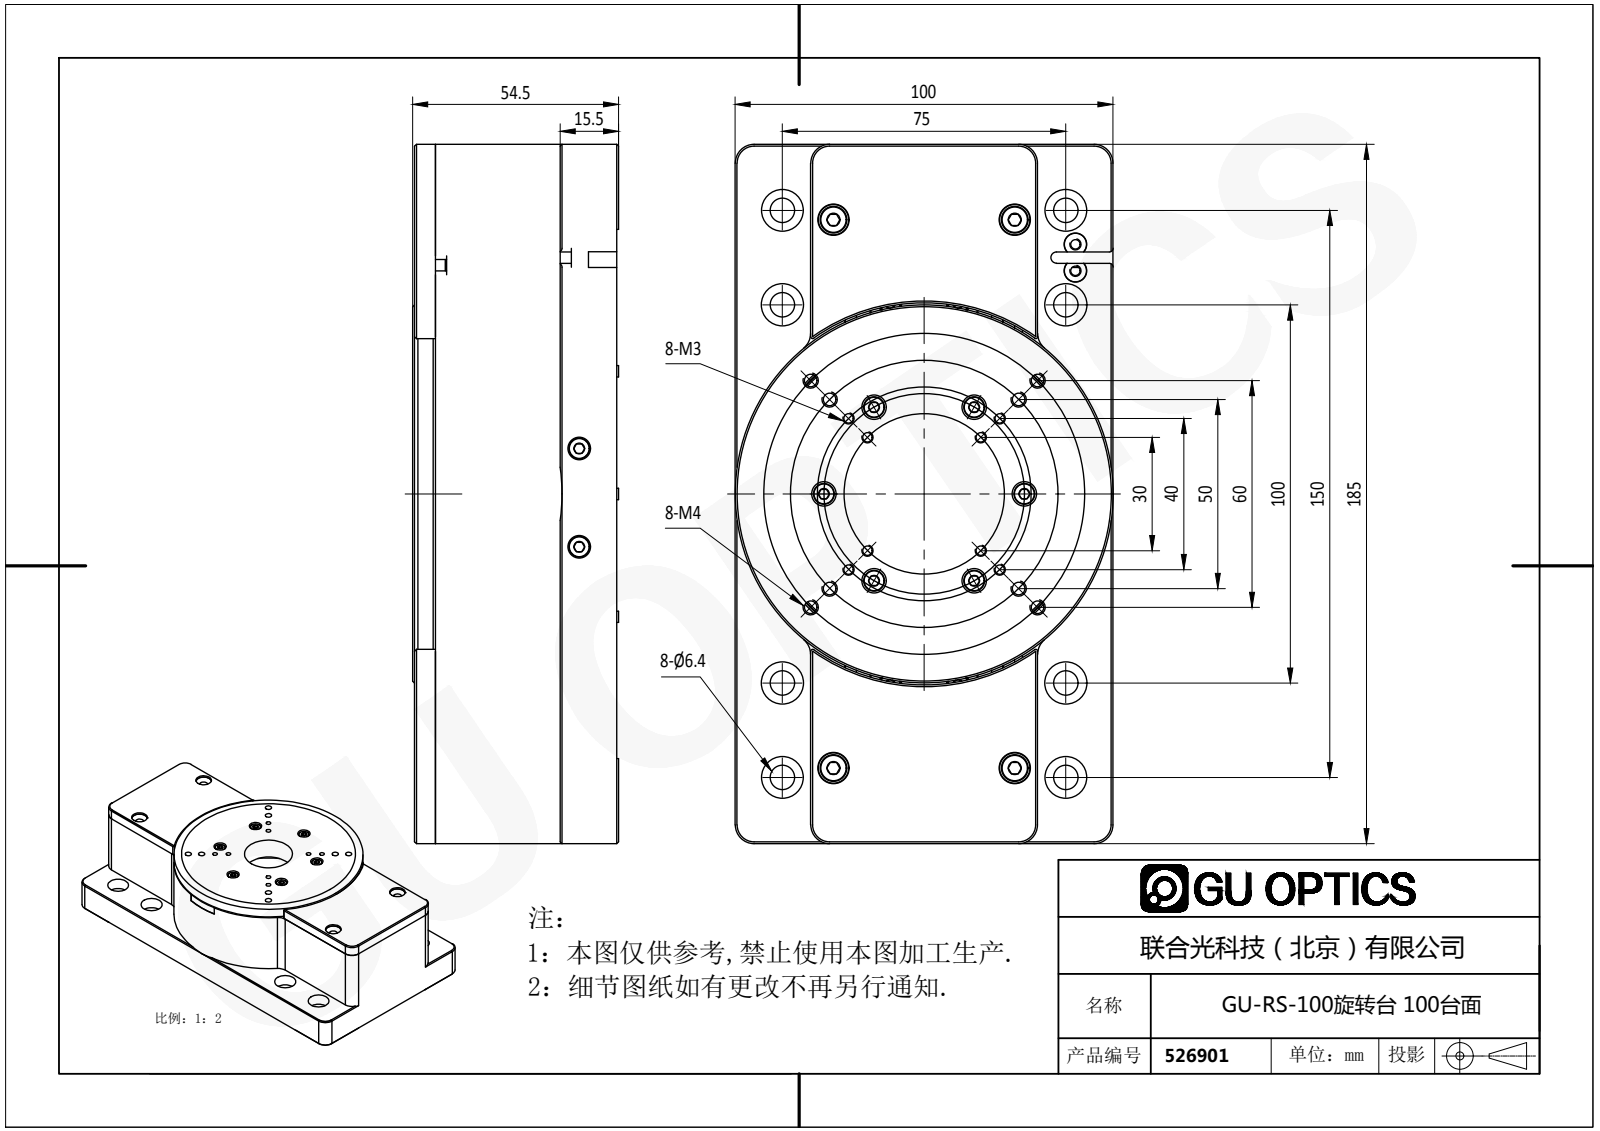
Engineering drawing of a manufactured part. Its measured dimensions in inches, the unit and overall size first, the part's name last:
Units: inches
Overall size (bounding box): 7.283 × 3.937 × 2.146
Round holes (diameter × count): ⌀0.098 ×40, ⌀0.13 ×12, ⌀0.252 ×8, ⌀0.126 ×6, ⌀0.256 ×6, ⌀0.081 ×4, ⌀0.106 ×4, ⌀0.118 ×4, ⌀0.157 ×4, ⌀0.169 ×4, ⌀0.197 ×4, ⌀0.325 ×4
Round bosses / shafts (diameter × count): ⌀0.118 ×48, ⌀0.217 ×8, ⌀0.157 ×8, ⌀0.128 ×4, ⌀0.098 ×4, ⌀0.097 ×4, ⌀0.097 ×4, ⌀3.937 ×1
Partial cylindrical surfaces — rounded edges, fillets, slot ends (radius × count): R0.118 ×30, R0.039 ×20, R0.197 ×16, R0.02 ×4, R0.079 ×4, R0.11 ×4, R0.059 ×3, R0.067 ×2
Main face-to-face distances: 1.89, 0.079, 0.02, 2.126, 1.811, 0.236, 1.299, 2.047, 0.61, 1.535
Hole centre spacings: 0.278, 1.043, 1.392, 0.557, 0.835, 1.623, 1.783, 1.867
Bodies: 0 solids, 1393 faces (522 planar, 529 cylindrical, 342 other)
STEP written by: SolidWorks 2016 (CONFIG_CONTROL_DESIGN)
